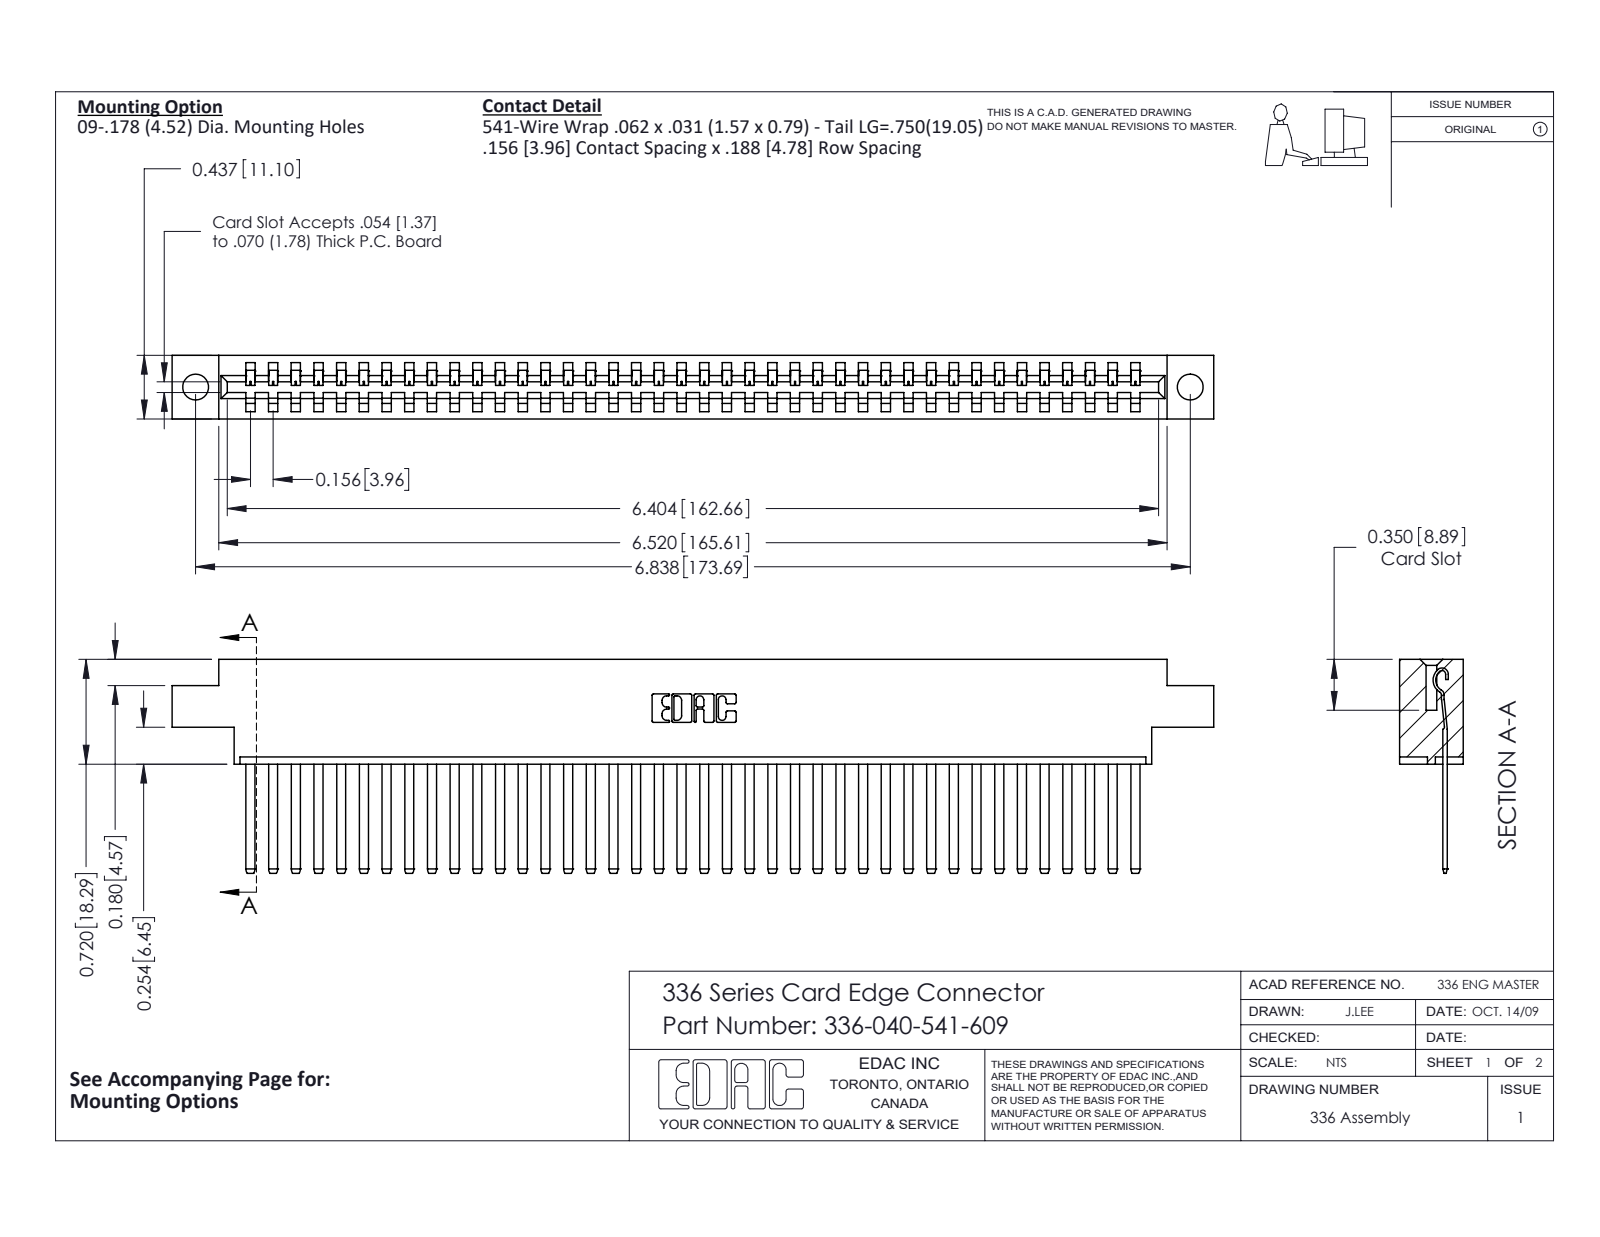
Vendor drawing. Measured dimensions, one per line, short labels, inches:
name: 336-290-001_336-290-541; 336 Part_Offset - .178 Dia - TH; 336-040-541-609
written by: SolidWorks 2020 (CONFIG_CONTROL_DESIGN)
unit: in
bodies: 41 solids, 2118 faces (1434 planar, 684 cylindrical, 0 other)
size: 7.161 × 1.47 × 0.437
volume: 1.605 in³; area: 44.26 in²
holes: 2× ⌀0.178
rounds: 80× R0.004, 80× R0.056, 22× R0.01, 6× R0.007, 6× R0.031, 3× R0.026, 2× R0.022, 2× R0.04
face distances: 0.437, 0.181, 0.328, 0.14, 0.297, 0.109, 0.031, 0.256, 0.05, 0.387
hole spacings: 6.838
